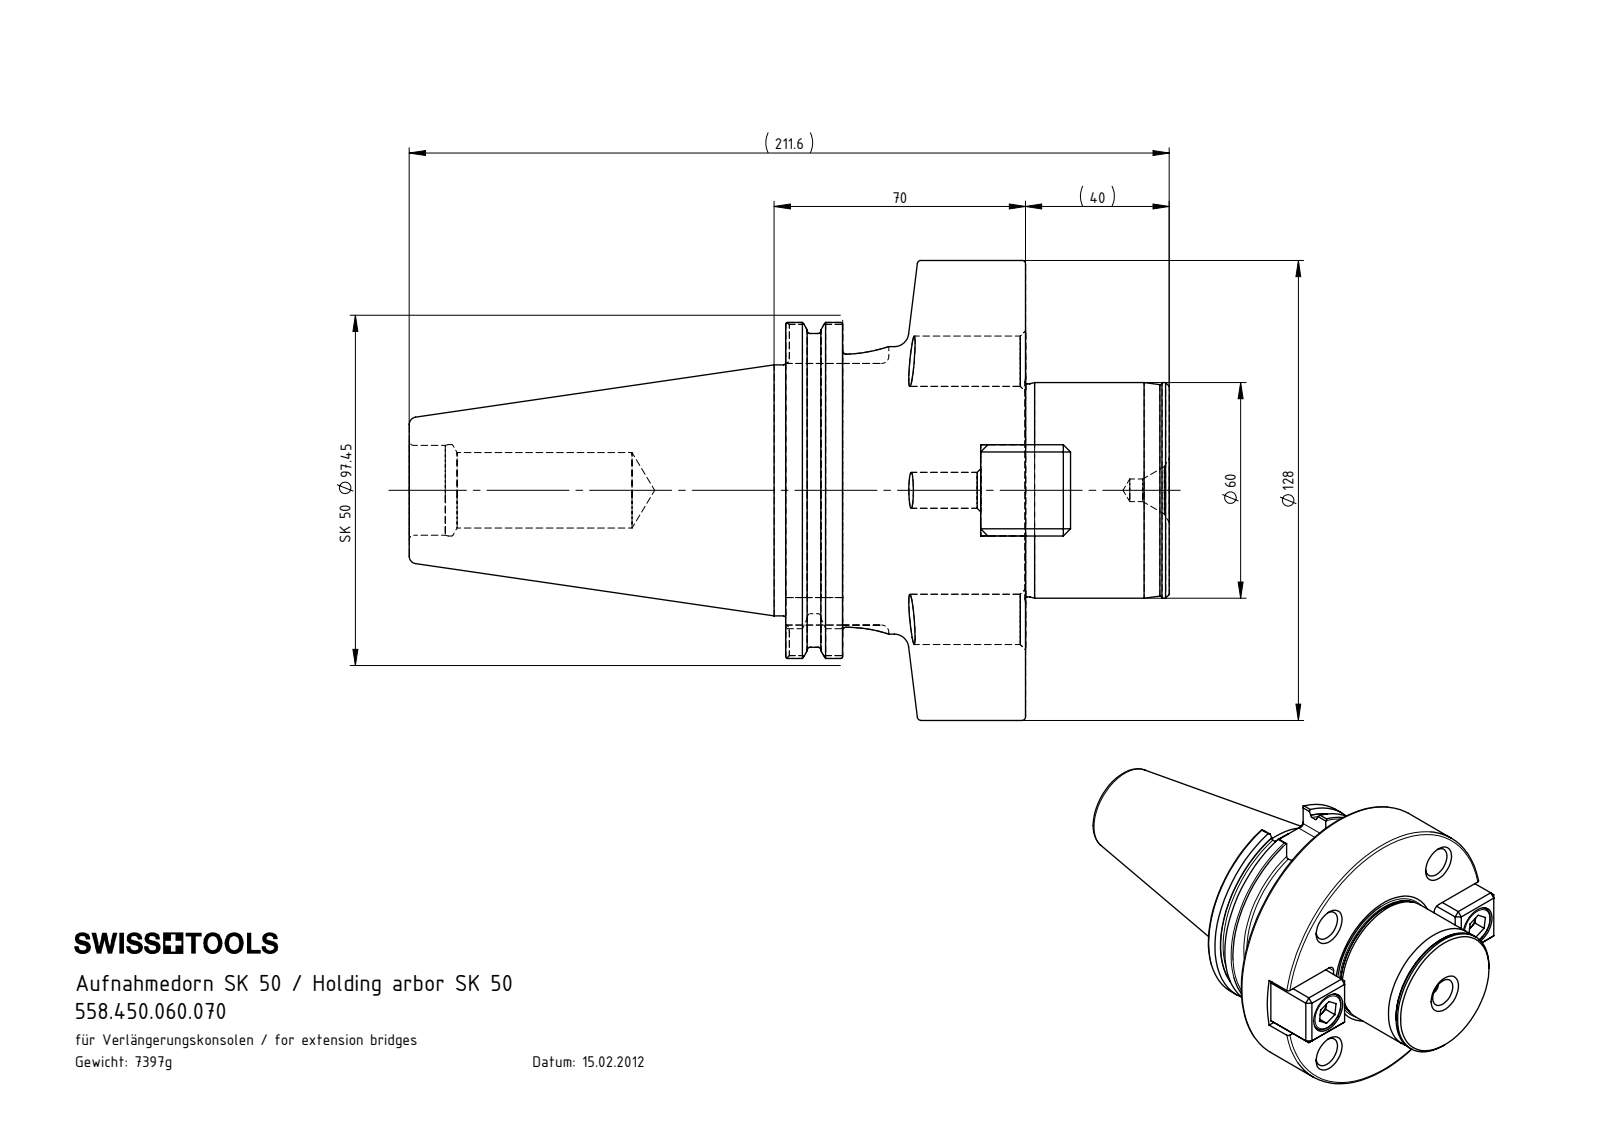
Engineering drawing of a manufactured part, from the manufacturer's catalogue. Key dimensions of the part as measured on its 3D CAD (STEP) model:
Part name (STEP PRODUCT): SK5-D60.K01.070_B; SK5-D60.K01.070; U00-D60.ER1.025; ISO 4762 - M12 x 25_PreviewCfg
STEP written by: SolidWorks 2017 (CONFIG_CONTROL_DESIGN)
Units: millimetres
Bodies: 5 solids, 292 faces (113 planar, 74 cylindrical, 105 other)
Overall size (bounding box): 211.6 × 128 × 128
Volume: 942 353 mm³ · Surface area: 99 476 mm²
Round holes (diameter × count): ⌀14 ×4, ⌀10 ×2, ⌀13 ×2, ⌀19 ×2, ⌀6.3 ×1, ⌀21 ×1, ⌀25 ×1, ⌀25.45 ×1
Round bosses / shafts (diameter × count): ⌀18 ×2, ⌀12 ×2, ⌀128 ×1, ⌀91 ×1, ⌀80 ×1, ⌀69.85 ×1, ⌀60 ×1, ⌀59.3 ×1
Partial cylindrical surfaces — rounded edges, fillets, slot ends (radius × count): R2 ×8, R3 ×4, R12.85 ×1, R48.73 ×1
Main face-to-face distances: 66.8, 25.4, 12.5, 106.8, 40, 54.3, 52.5, 15.85, 38.45, 50.95
Hole centre spacings: 38.23, 50.8, 71.84, 92.2, 49, 101.6, 98
